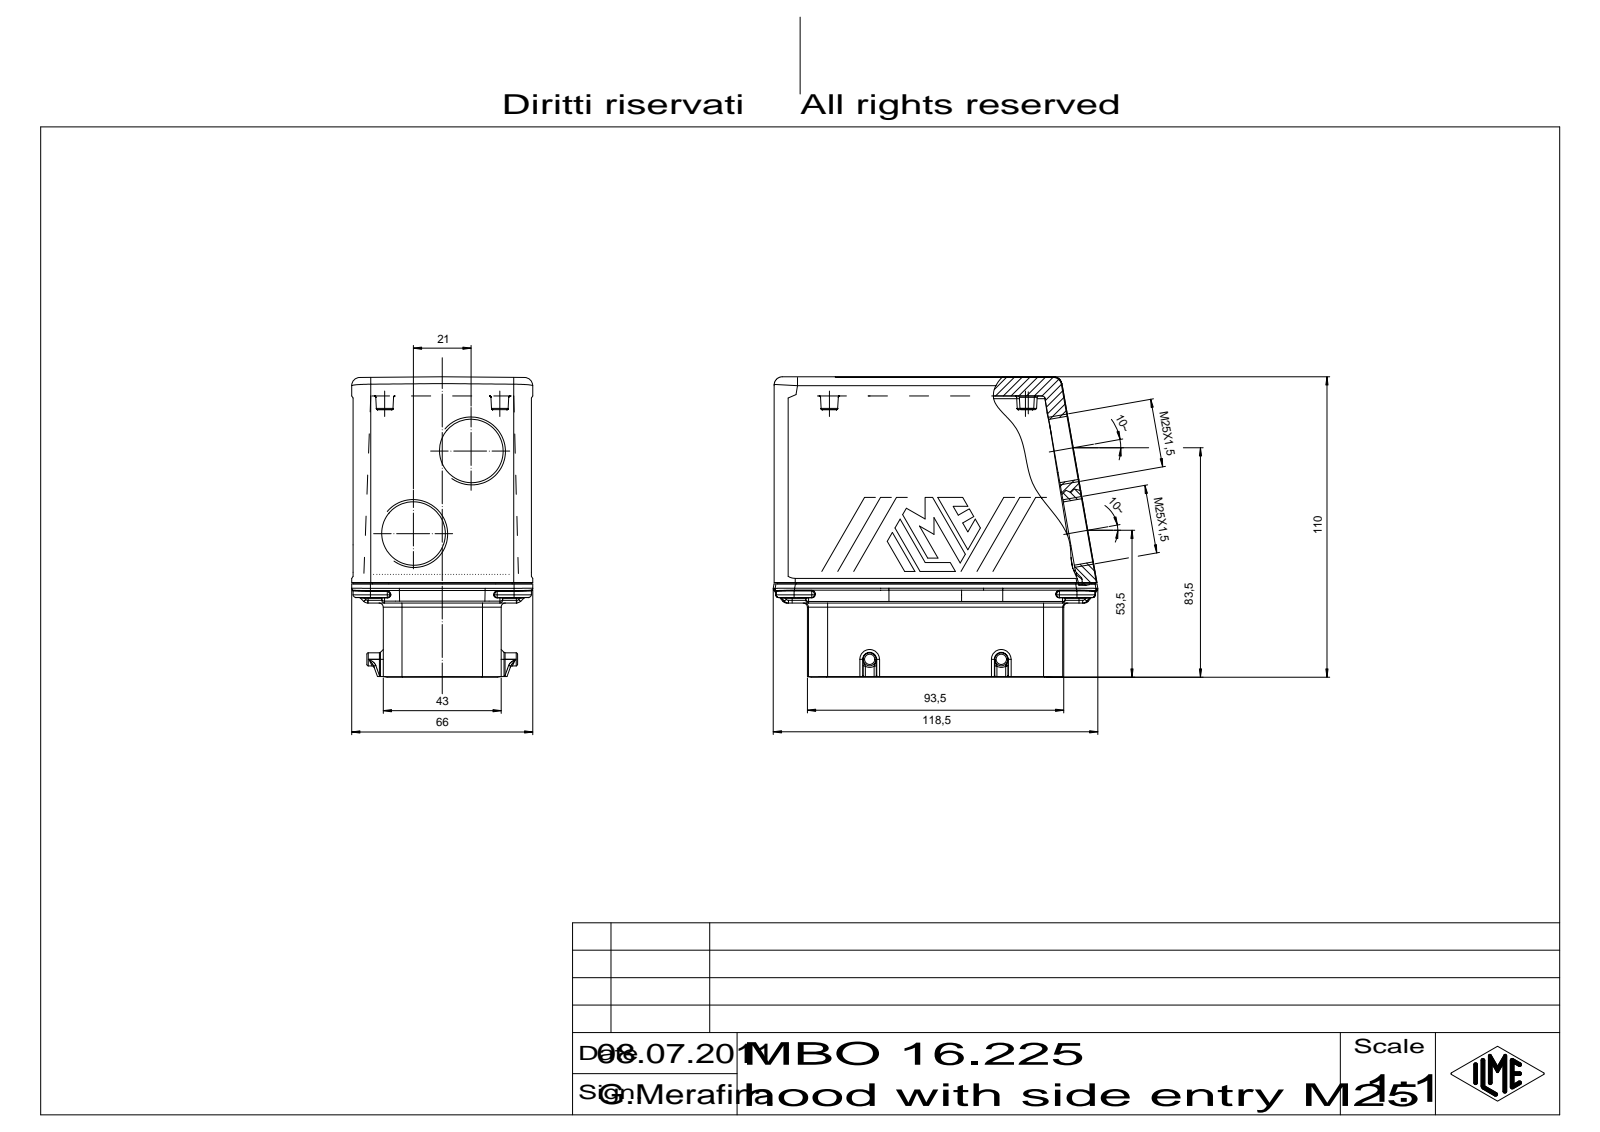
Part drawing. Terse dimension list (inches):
name: 53848_Body_1
written by: CoCreate Modeling 16.00A 16-Aug-2008 (C) Parametric Technology GmbH (AUTOMOTIVE_DESIGN)
unit: in
bodies: 1 solid, 650 faces (334 planar, 152 cylindrical, 164 other)
size: 4.617 × 4.29 × 2.599
volume: 35.81 in³; area: 94.3 in²
holes: 2× ⌀0.984
bosses: 2× ⌀0.189
rounds: 44× R0.039, 18× R0.012, 12× R0.276, 10× R0.118, 8× R0.02, 6× R0.059, 4× R0.165, 4× R0.197
face distances: 2.559, 3.237, 0.016, 2.575, 0.433, 2.126, 2.126, 1.693, 0.433, 0.449
hole spacings: 1.444
